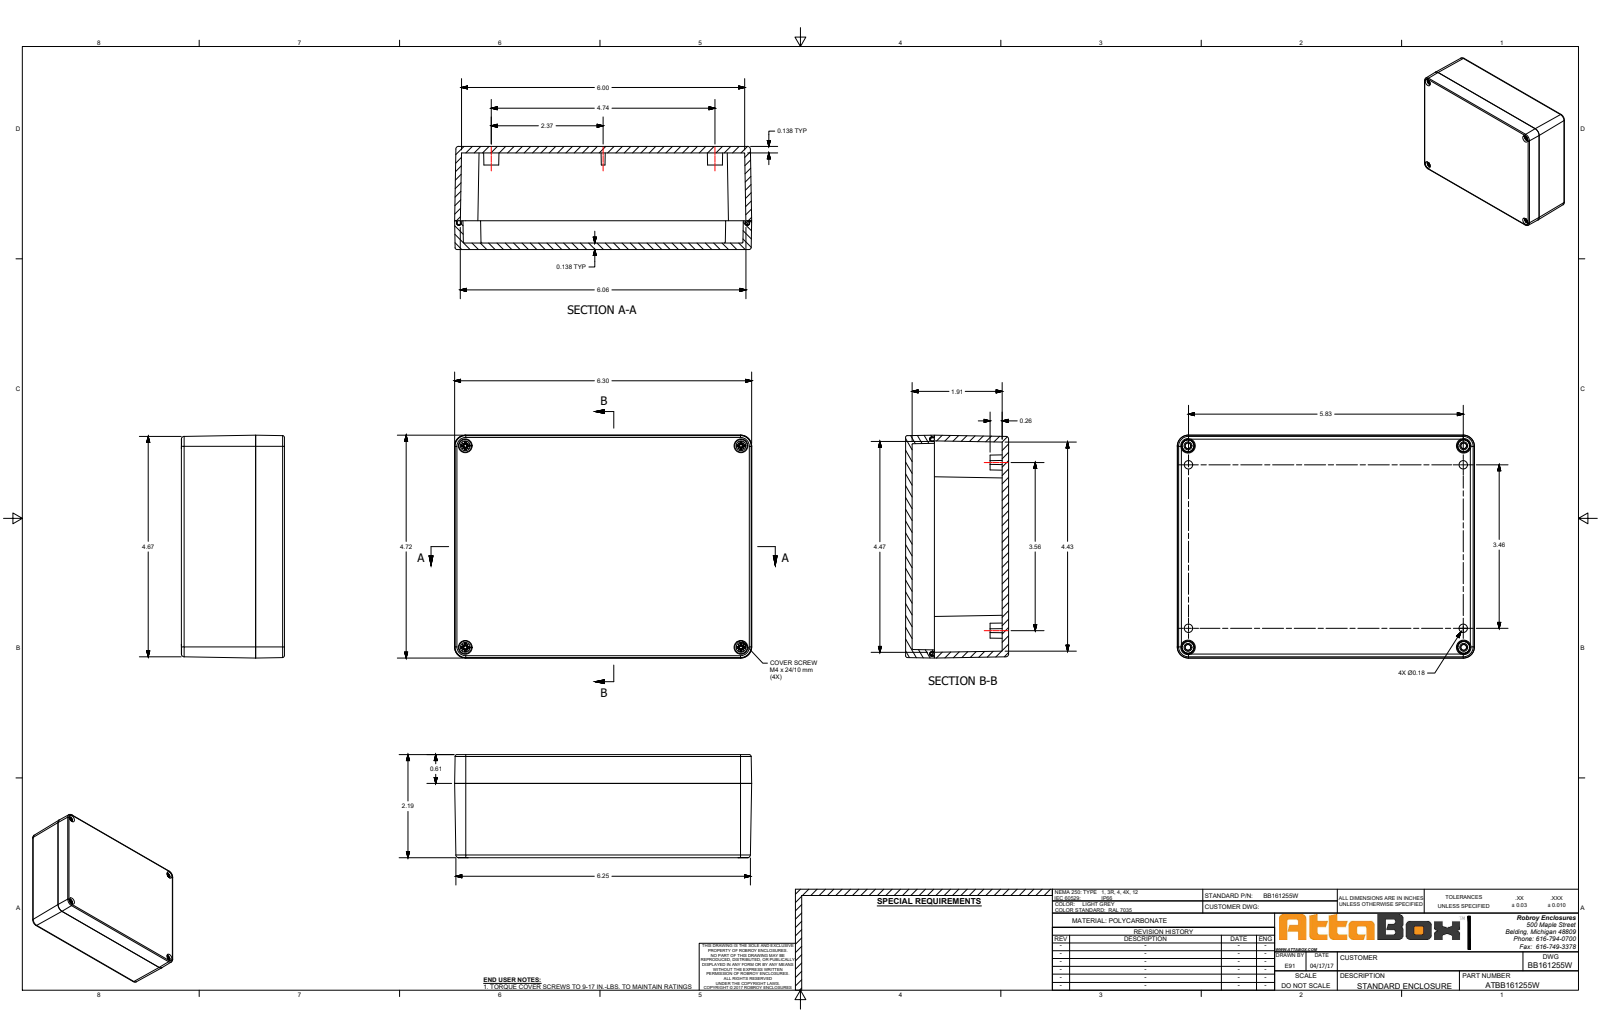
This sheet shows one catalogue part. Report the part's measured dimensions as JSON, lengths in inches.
{"part_name": "BB161255W", "step_written_by": "SolidWorks 2018 (AUTOMOTIVE_DESIGN)", "units": "inches", "bodies": {"solids": 11, "faces": 1555, "planar": 585, "cylindrical": 396, "other": 574}, "overall_size": [6.299, 4.724, 2.185], "volume_in3": 14.32, "surface_area_in2": 240.3, "round_holes": [[0.177, 8], [0.128, 4], [0.189, 4], [0.201, 4], [0.276, 4], [0.291, 4], [0.307, 4]], "round_bosses_or_shafts": [[0.268, 4], [0.173, 4], [0.157, 4], [0.13, 4]], "partial_cylinders_radius": [[0.039, 40], [0.02, 30], [0.098, 8], [0.193, 8], [0.059, 4], [0.102, 4], [0.124, 4], [0.14, 4]], "face_to_face_distances": [0.138, 2.047, 2.185, 1.909, 0.122, 4.724, 4.602, 4.551, 6.177, 6.299], "hole_center_spacings": [0.404, 3.868, 5.85, 7.002, 3.465, 4.272, 5.827, 5.846]}
